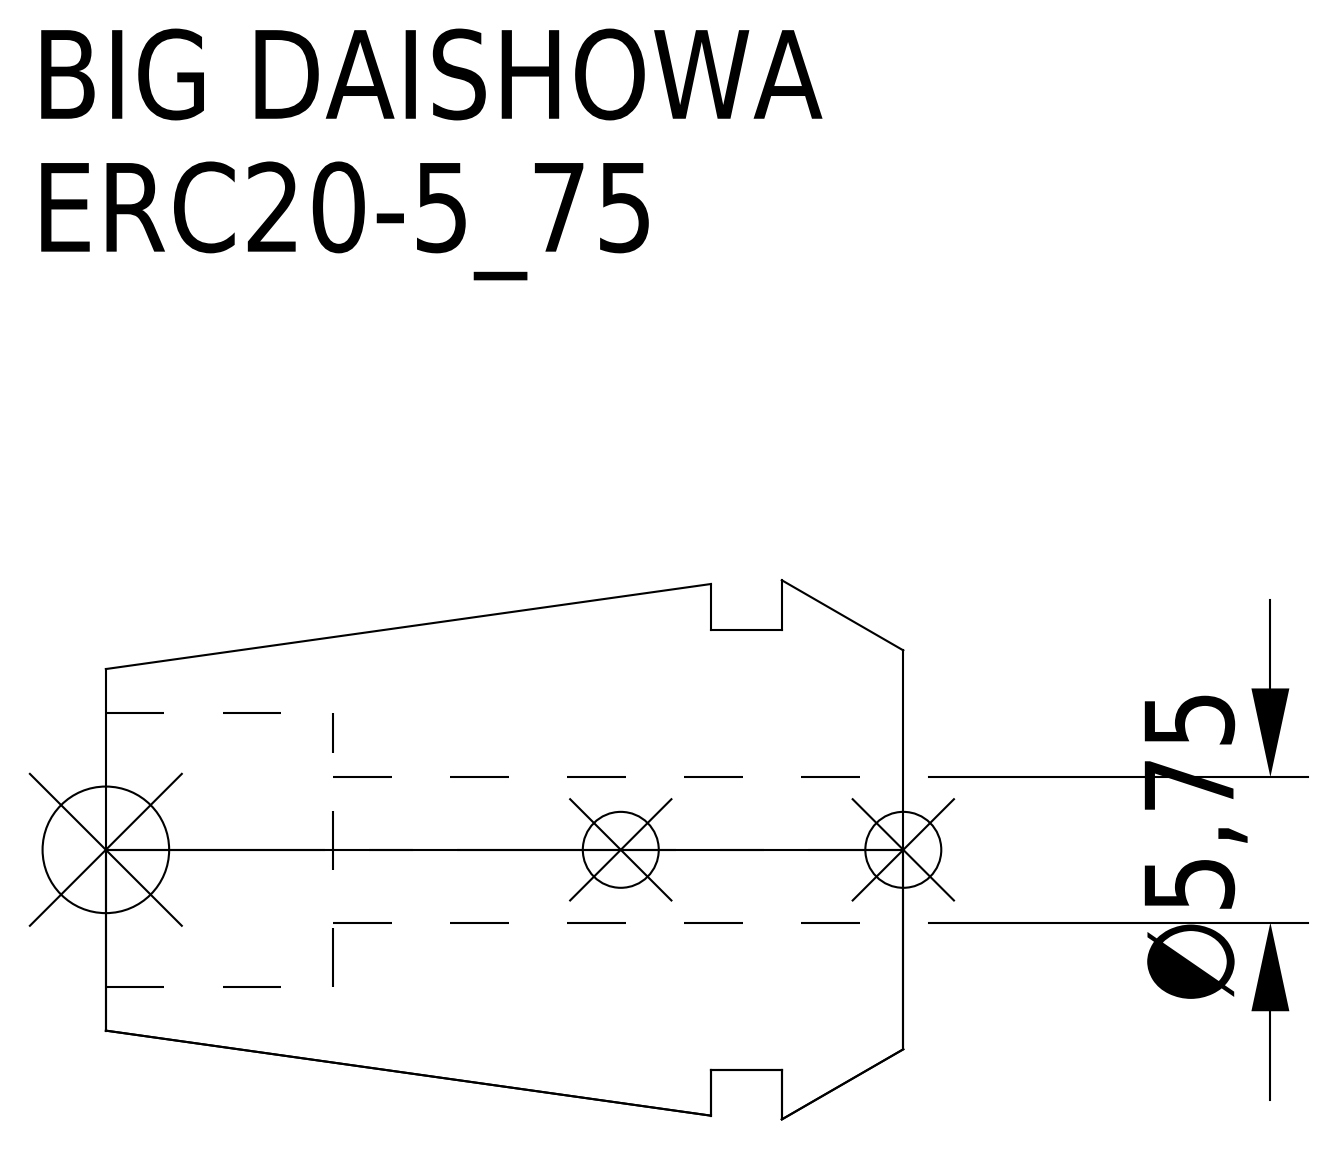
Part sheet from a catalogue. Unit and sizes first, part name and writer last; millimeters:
Units: millimetres
Overall size (bounding box): 31.5 × 21.3 × 21.3
Round holes (diameter × count): ⌀5.75 ×1, ⌀10.8 ×1
Round bosses / shafts (diameter × count): ⌀17.4 ×1
Main face-to-face distances: 4.8, 7.6, 2.8, 31.5, 26.7, 23.9, 22.52, 17.72, 14.92, 8.98
Volume: 6 475 mm³ · Surface area: 3 055 mm²
Bodies: 1 solid, 15 faces (5 planar, 6 cylindrical, 4 other)
Part name (STEP PRODUCT): ERC20-5_75
STEP written by: CREO PARAMETRIC BY PTC INC, 2016380 (AUTOMOTIVE_DESIGN)
